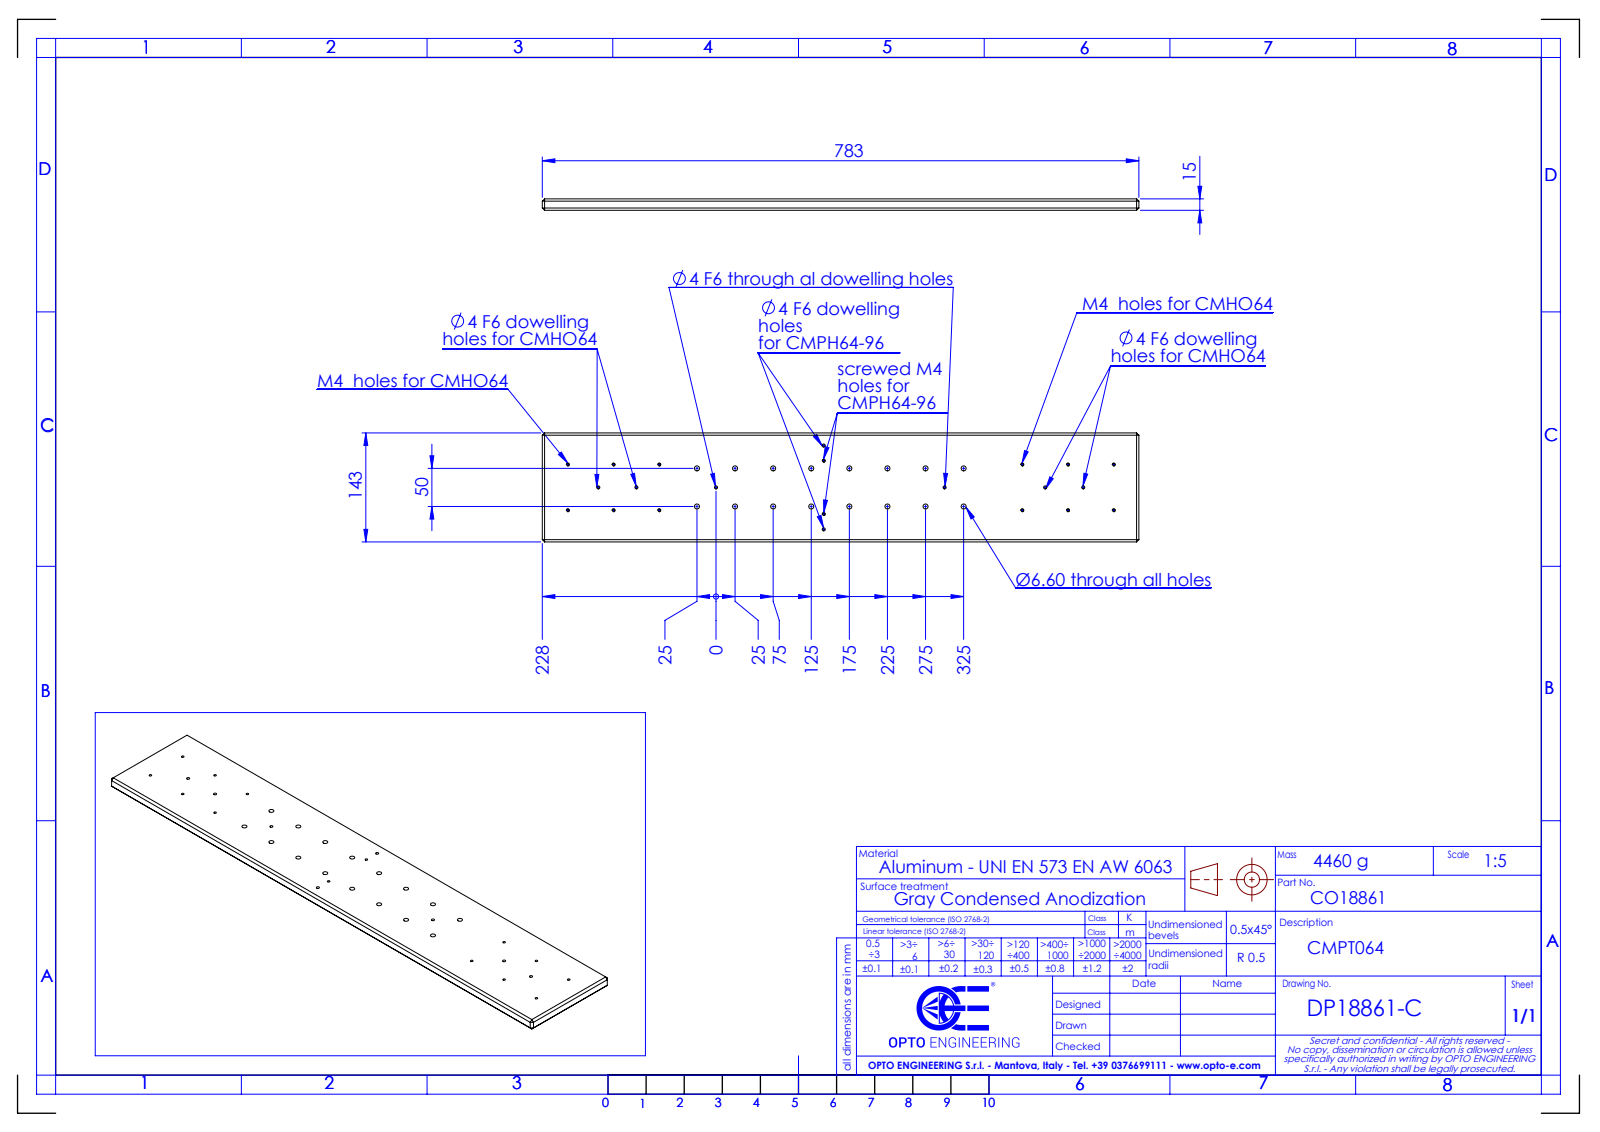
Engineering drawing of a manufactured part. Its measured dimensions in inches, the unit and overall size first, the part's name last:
Units: inches
Overall size (bounding box): 30.827 × 5.63 × 0.591
Round holes (diameter × count): ⌀0.26 ×16, ⌀0.13 ×14, ⌀0.157 ×8
Main face-to-face distances: 0.591, 5.63, 4.231, 30.827, 22.045, 25.608, 0.394, 0.197, 21.104, 0.217
Hole centre spacings: 1.969, 2.784, 3.937, 4.402, 5.906, 6.225, 1.392, 7.874
Volume: 100.8 in³ · Surface area: 390.4 in²
Bodies: 1 solid, 108 faces (32 planar, 76 cylindrical, 0 other)
Part name (STEP PRODUCT): DP18861-C_CMPT064
STEP written by: SolidWorks 2021 (AUTOMOTIVE_DESIGN)
